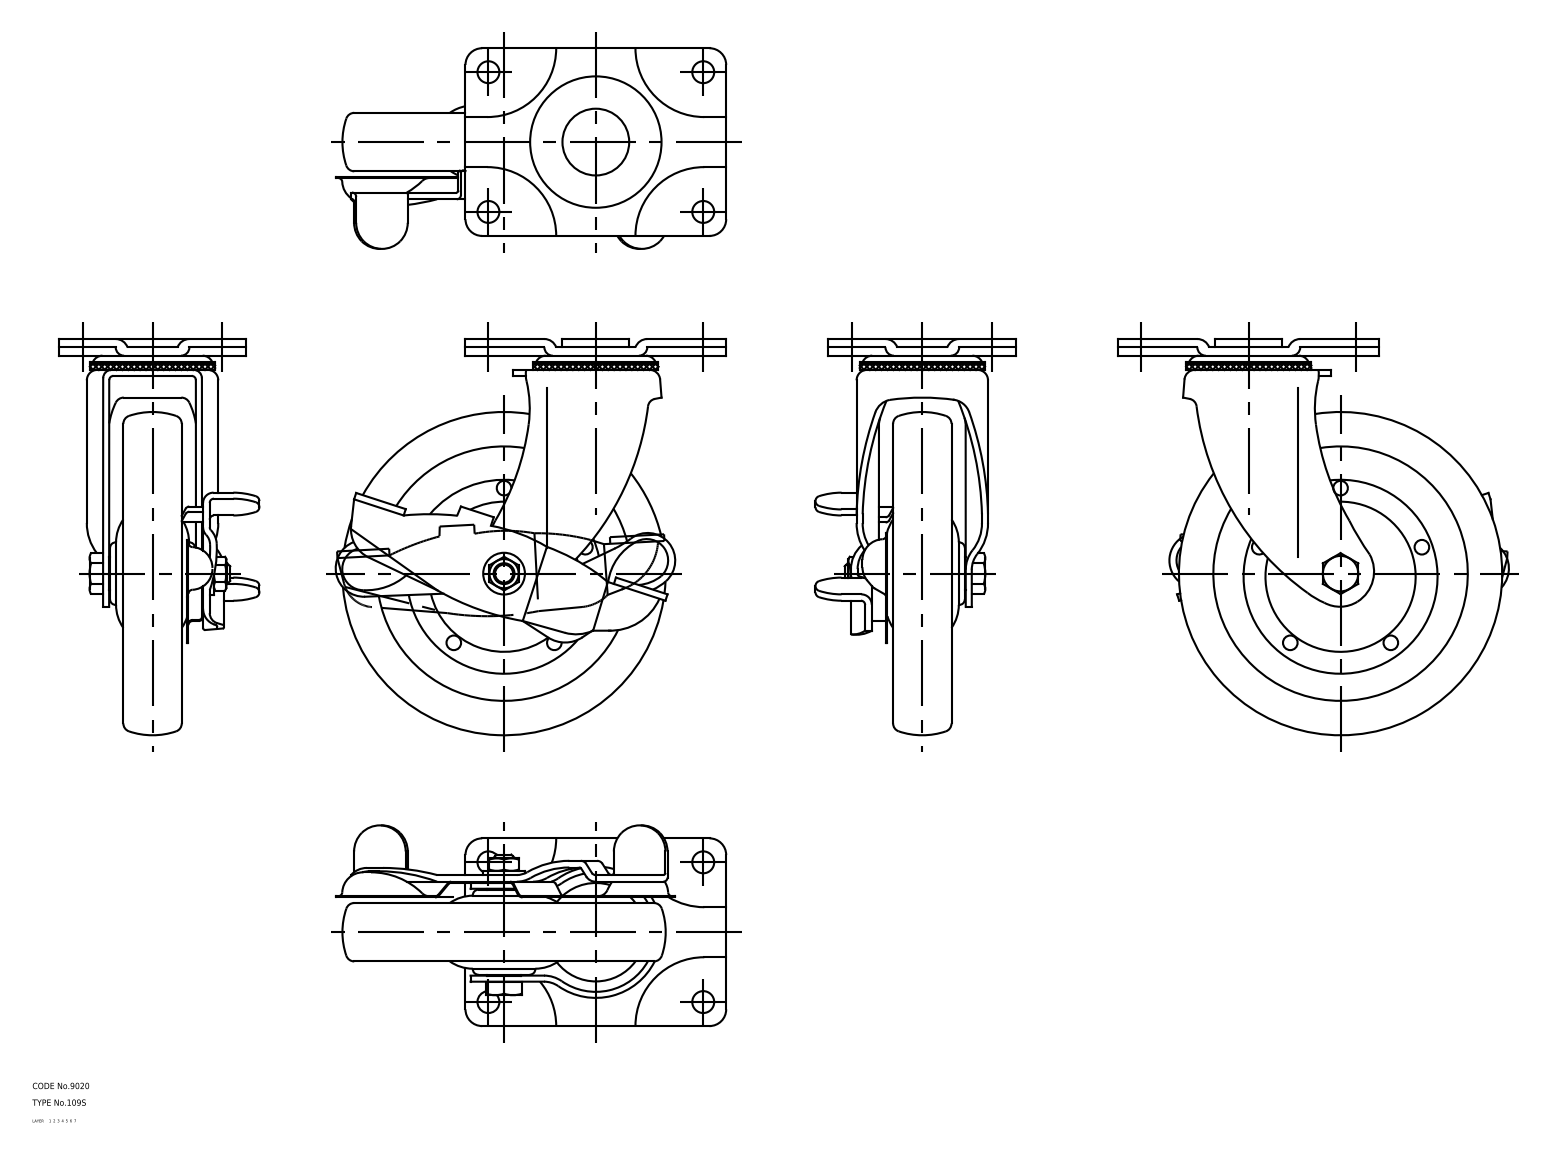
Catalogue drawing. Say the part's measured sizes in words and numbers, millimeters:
The part is named "67139298; 67139311; 67139324; 67139337 (+6 more)". Its 3-D file was written by "CADfix (AUTOMOTIVE_DESIGN)". It is 7 solids with 468 faces: 0 planar, 0 cylindrical and 468 other. Overall it measures 190 by 187.22 by 96.22 millimeters. Its volume is 581 763 cubic millimeters and its surface area 143 660 square millimeters.
